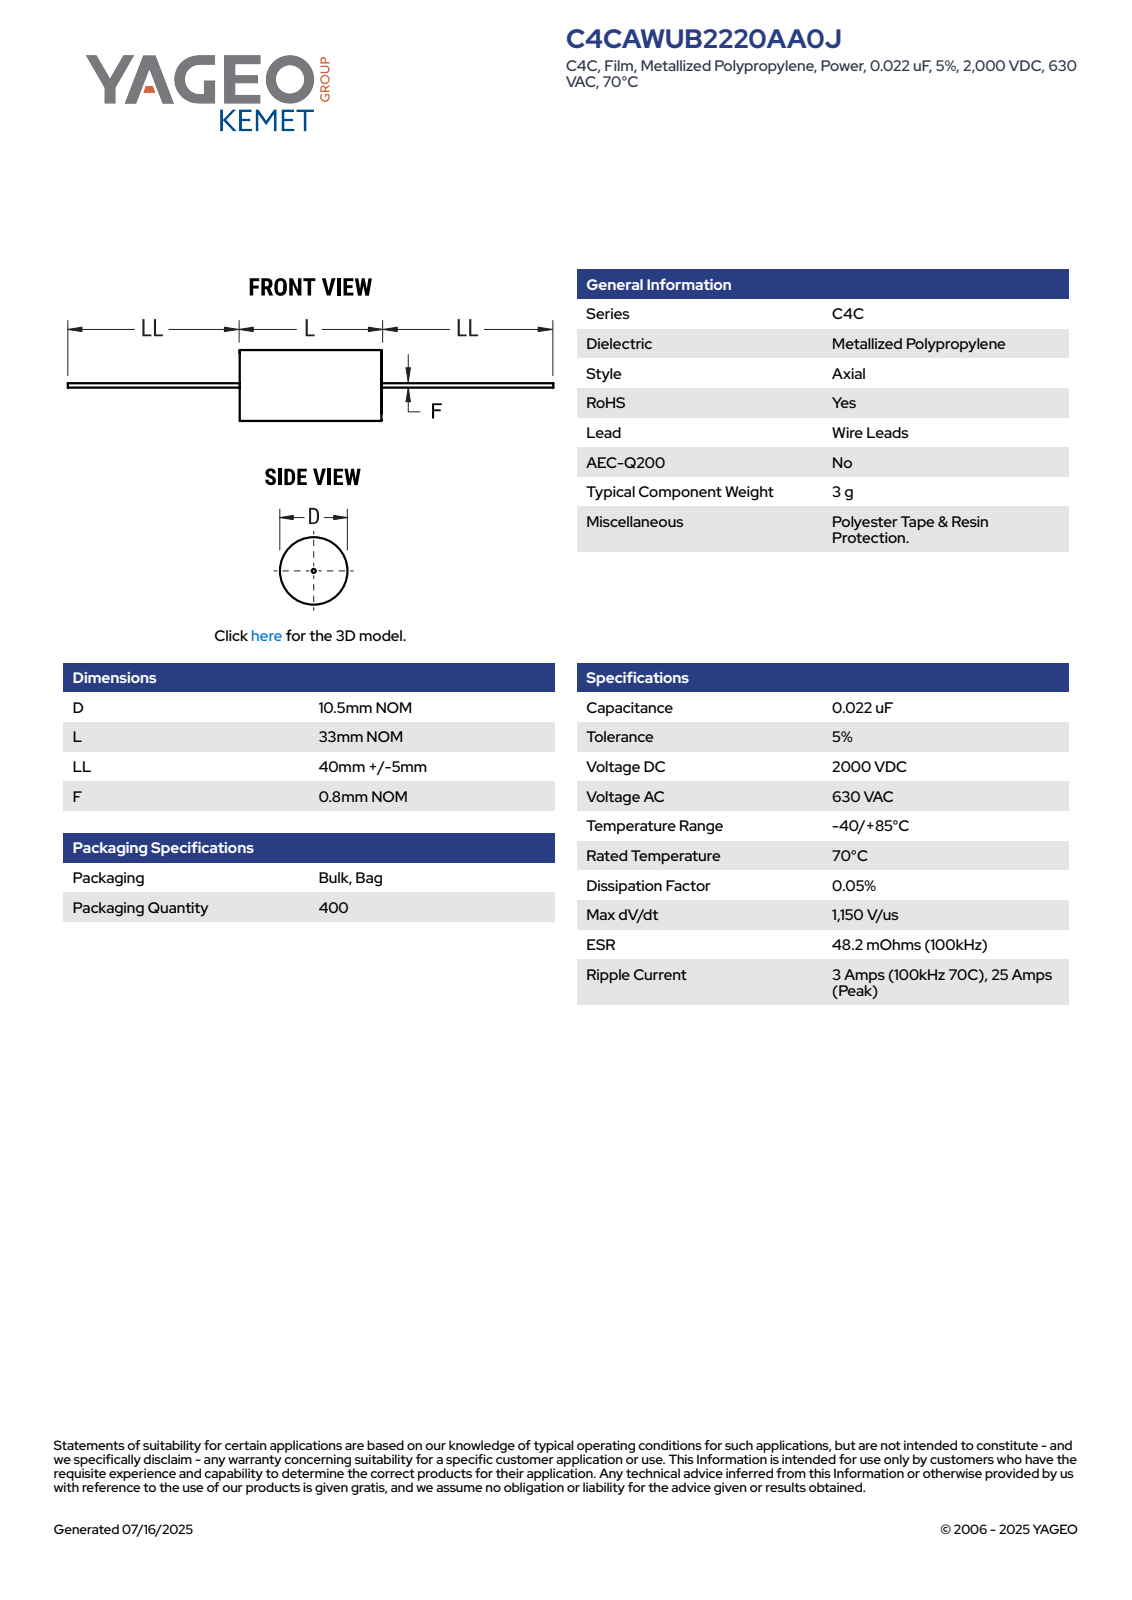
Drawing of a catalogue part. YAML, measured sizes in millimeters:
part_name: "CFP_ACWF_10.5X33_D10.5L33LL45F0.8"
step_written_by: "SolidWorks 2014 (AUTOMOTIVE_DESIGN)"
units: millimeters
bodies: {solids: 2, faces: 87, planar: 28, cylindrical: 28, other: 31}
overall_size: [123, 10.5, 10.5]
volume: 2902
surface_area: 1661
round_bosses_or_shafts:
  - {diameter: 10.5, count: 1}
  - {diameter: 0.8, count: 1}
partial_cylinders:
  - {radius: 5.24, count: 1}
face_to_face_distances: [33.01, 33, 45, 78, 44.99, 123, 78.01]
